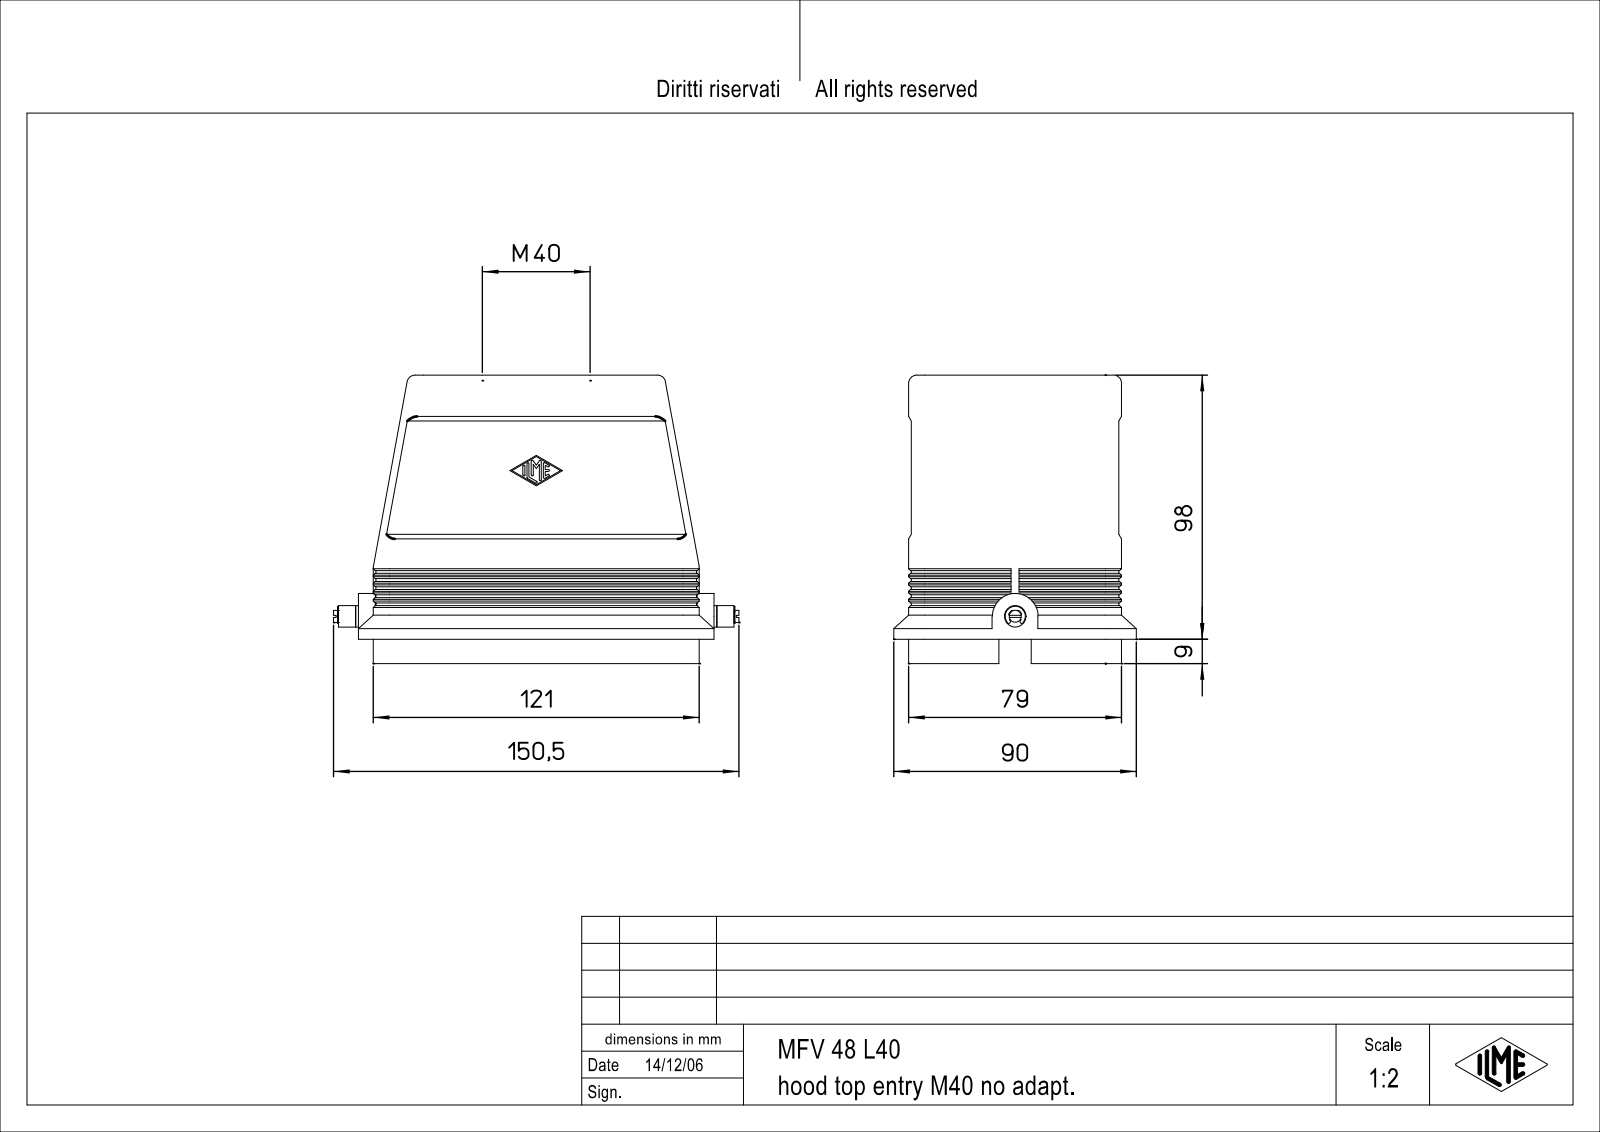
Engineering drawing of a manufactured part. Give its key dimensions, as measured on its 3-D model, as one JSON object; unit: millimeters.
{"part_name": "CH_MH Tüllengehäuse Verschluss für 1 Bügel 104_62 Teil 2", "step_written_by": "Autodesk Inventor 7 (AUTOMOTIVE_DESIGN)", "units": "millimeters", "bodies": {"solids": 1, "faces": 672, "planar": 246, "cylindrical": 177, "other": 249}, "overall_size": [150.5, 118, 90], "volume_mm3": 229063, "surface_area_mm2": 106739, "round_holes": [[2.46, 4], [3.5, 4], [40, 1], [56, 1]], "round_bosses_or_shafts": [[8, 1], [6, 1], [4.5, 1], [3.5, 1]], "partial_cylinders_radius": [[0.38, 14], [2, 12], [6, 10], [0.5, 4], [3, 4], [11.5, 4], [0.95, 3], [0.62, 2]], "face_to_face_distances": [3.5, 72, 75.5, 1, 109, 2.5, 79, 74.5, 78, 9], "hole_center_spacings": [27, 52.15, 60.54, 104, 107.45]}
